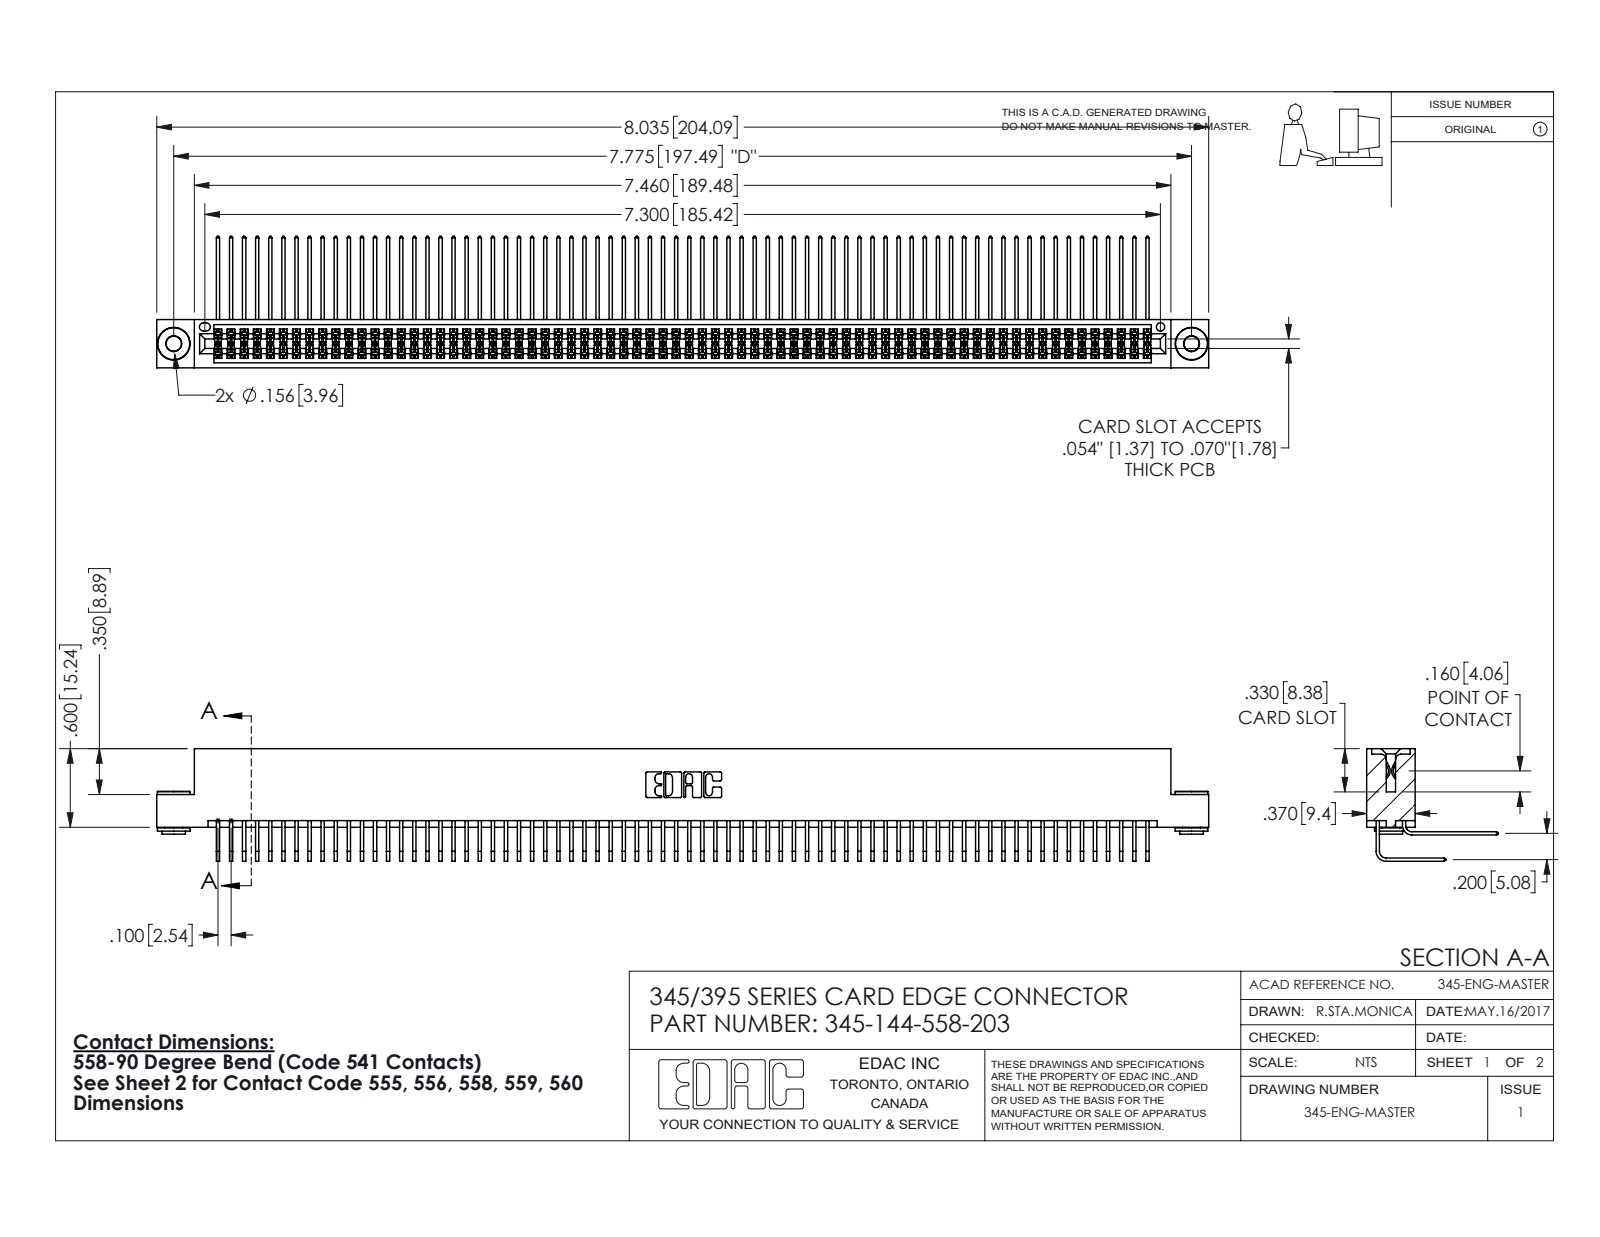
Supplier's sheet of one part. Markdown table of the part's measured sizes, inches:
| quantity | value |
| --- | --- |
| part name | 345-292-001_558 559 Tail - 1; 345-144-558-203; 345 Part_Flush Mounting Lugs - 0.156 Dia-TH; 345-250-002_345-250-002-102 (+1 more) |
| STEP written by | SolidWorks 2016 (CONFIG_CONTROL_DESIGN) |
| units | inches |
| bodies | 147 solids, 7652 faces (5130 planar, 2514 cylindrical, 8 other) |
| overall size | 8.035 × 1.005 × 0.859 |
| volume | 1.279 in³ |
| surface area | 55.28 in² |
| round holes (diameter × count) | 0.116 × 2, 0.156 × 2, 0.064 × 1 |
| round bosses / shafts (diameter × count) | 0.25 × 2, 0.18 × 2, 0.136 × 2 |
| partial cylindrical surfaces (radius × count) | 0.006 × 288, 0.01 × 22, 0.007 × 6, 0.031 × 6, 0.026 × 3, 0.014 × 2, 0.019 × 2, 0.022 × 2 |
| main face-to-face distances | 0.072, 0.298, 0.2, 0.37, 0.025, 0.098, 0.272, 0.225, 0.025, 0.175 |
| hole center spacings | 0.27, 7.539, 7.775 |
